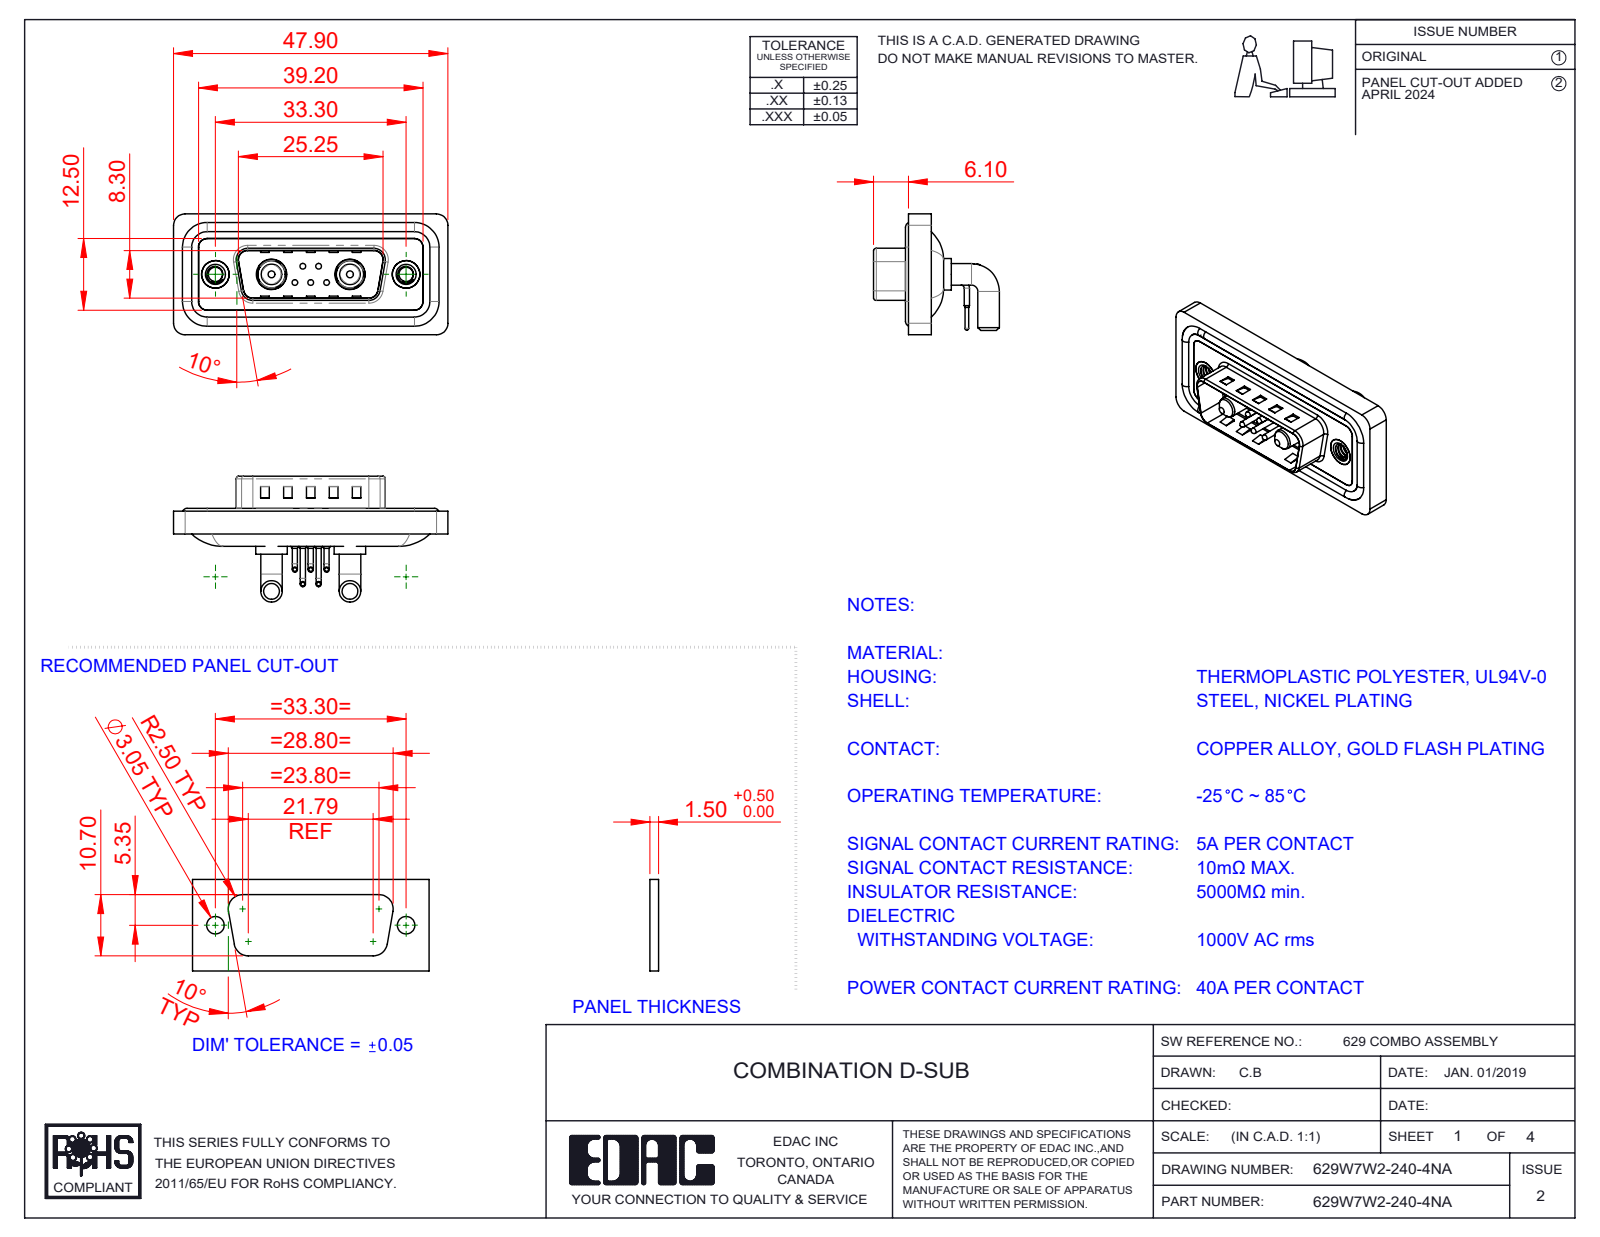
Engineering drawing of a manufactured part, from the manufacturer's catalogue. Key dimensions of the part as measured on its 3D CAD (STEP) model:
Part name (STEP PRODUCT): 629Combo Contact Row 1; 629Combo Shell Rear_15 Contacts; 629Combo Contact Row 2; 629W7W2-140-4NA (+5 more)
STEP written by: SolidWorks 2023 (CONFIG_CONTROL_DESIGN)
Units: millimetres
Bodies: 16 solids, 1077 faces (517 planar, 404 cylindrical, 156 other)
Overall size (bounding box): 47.9 × 21.98 × 21.1
Volume: 5 830 mm³ · Surface area: 9 232 mm²
Round holes (diameter × count): ⌀0.75 ×5, ⌀1.6 ×5, ⌀2 ×5, ⌀2.5 ×2, ⌀4 ×2, ⌀4.8 ×2, ⌀4.85 ×2, ⌀5 ×2, ⌀5.3 ×2
Round bosses / shafts (diameter × count): ⌀0.9 ×10, ⌀1.5 ×5, ⌀1 ×5, ⌀0.65 ×5, ⌀3.75 ×4, ⌀1.6 ×4, ⌀5.5 ×2, ⌀5.2 ×2
Partial cylindrical surfaces — rounded edges, fillets, slot ends (radius × count): R2 ×20, R1.5 ×18, R0.5 ×8, R1.6 ×8, R1.01 ×5, R0.25 ×4, R0.6 ×4, R0.65 ×4
Main face-to-face distances: 0.4, 2.9, 0.8, 1.1, 2.1, 1.6, 2.5, 3.1, 4.5, 4.1
Hole centre spacings: 3.16, 2.77, 9.8, 23.5, 4.31, 4.33, 5.03, 5.04
